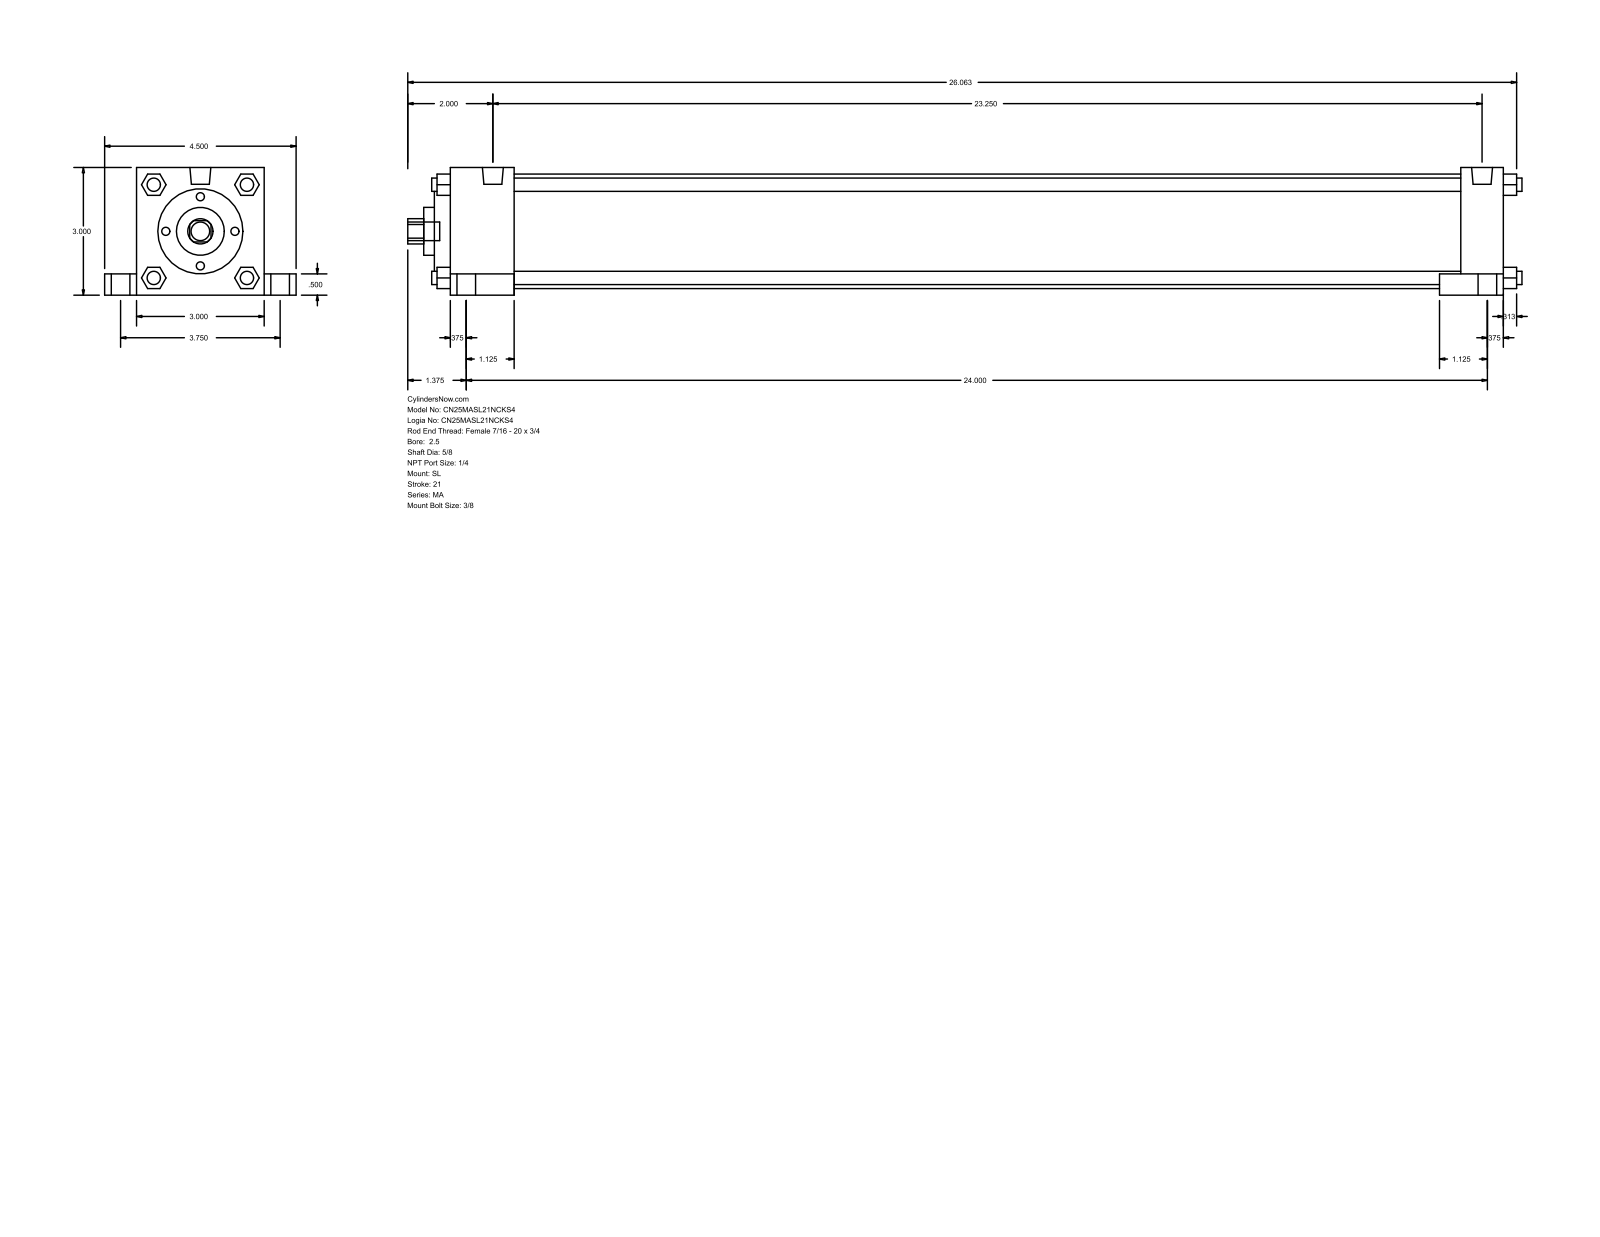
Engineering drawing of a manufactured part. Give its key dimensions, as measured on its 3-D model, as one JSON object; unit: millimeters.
{"part_name": "MA_SL__0250_0.625", "step_written_by": "GSSL Pune (CONFIG_CONTROL_DESIGN)", "units": "millimeters", "bodies": {"solids": 0, "faces": 150, "planar": 113, "cylindrical": 37, "other": 0}, "overall_size": [665.16, 114.3, 76.2], "round_holes": [[15.88, 1], [28.57, 1], [50.8, 1], [68.33, 1]], "round_bosses_or_shafts": [[7.94, 8], [11.11, 5], [17.46, 4], [12.49, 2]], "partial_cylinders_radius": [[7.54, 1]], "face_to_face_distances": [76.2, 628.65, 12.7, 565.15, 25.4, 38.1, 590.55, 603.25, 19.05, 63.5]}
